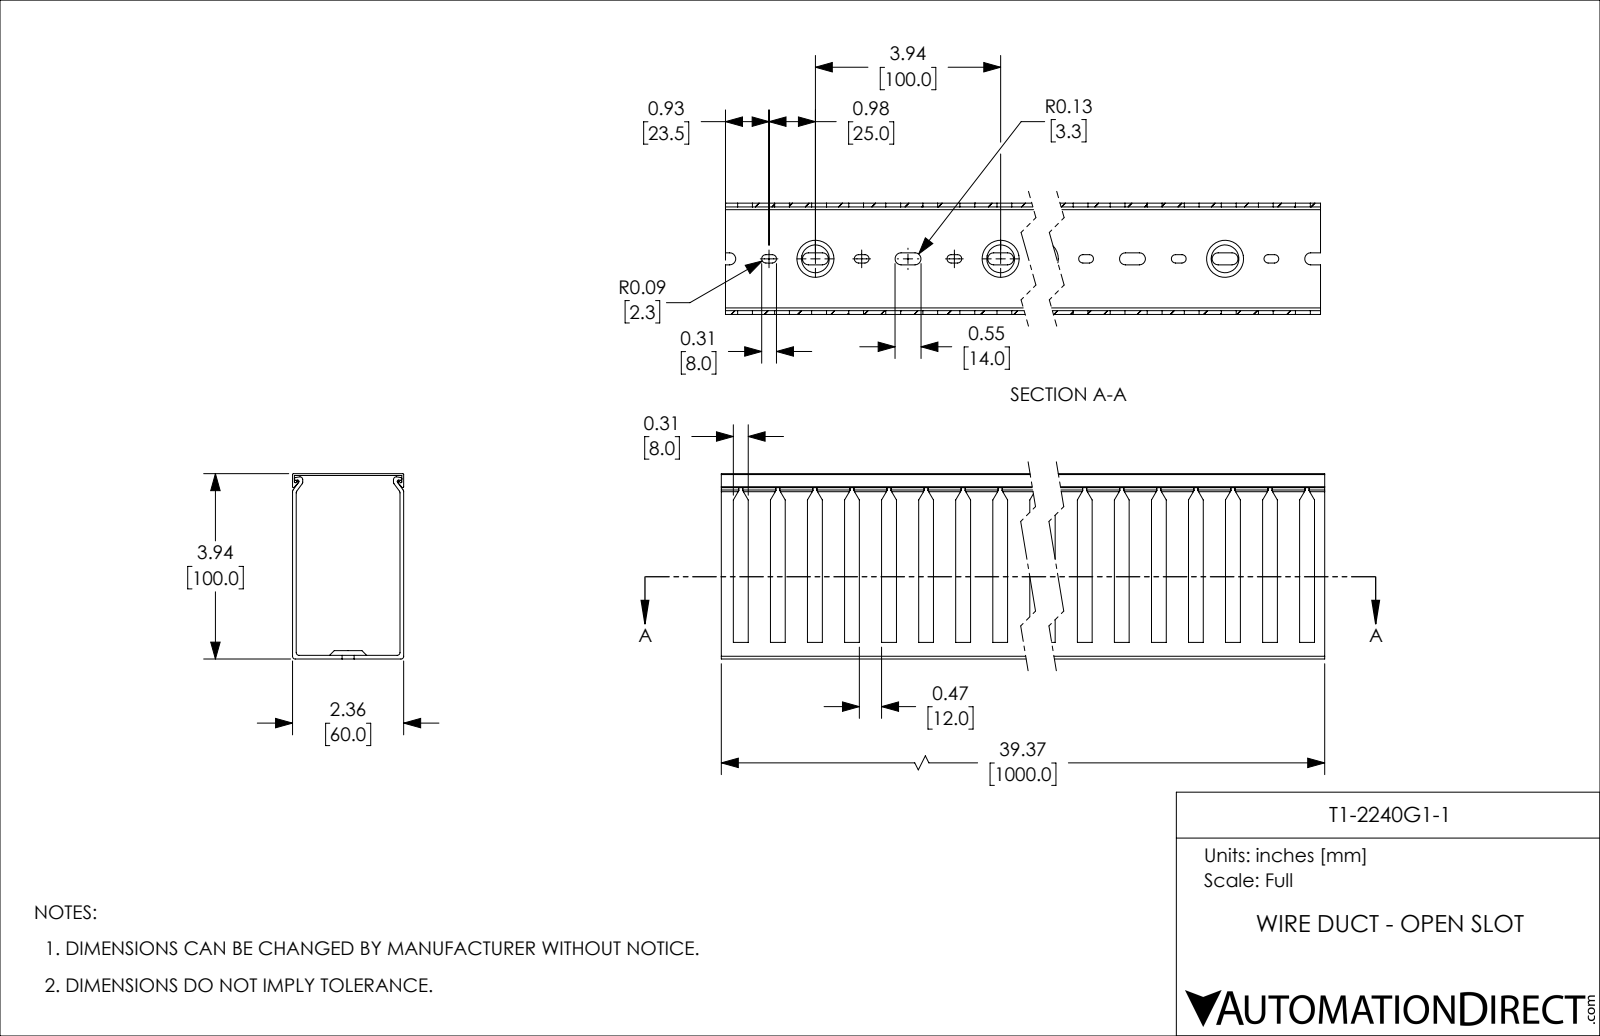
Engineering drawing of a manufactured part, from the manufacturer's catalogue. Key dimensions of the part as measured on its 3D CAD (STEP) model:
Part name (STEP PRODUCT): T1-2240G1-1
STEP written by: SolidWorks 2021 (CONFIG_CONTROL_DESIGN)
Units: millimetres
Bodies: 2 solids, 775 faces (444 planar, 311 cylindrical, 20 other)
Overall size (bounding box): 1000 × 100 × 60
Volume: 567 061 mm³ · Surface area: 651 643 mm²
Partial cylindrical surfaces — rounded edges, fillets, slot ends (radius × count): R2.25 ×40, R3.25 ×40, R1.5 ×12, R0.5 ×8, R0.75 ×6
Main face-to-face distances: 2, 58, 60, 56, 1, 100, 99, 97, 98, 59
